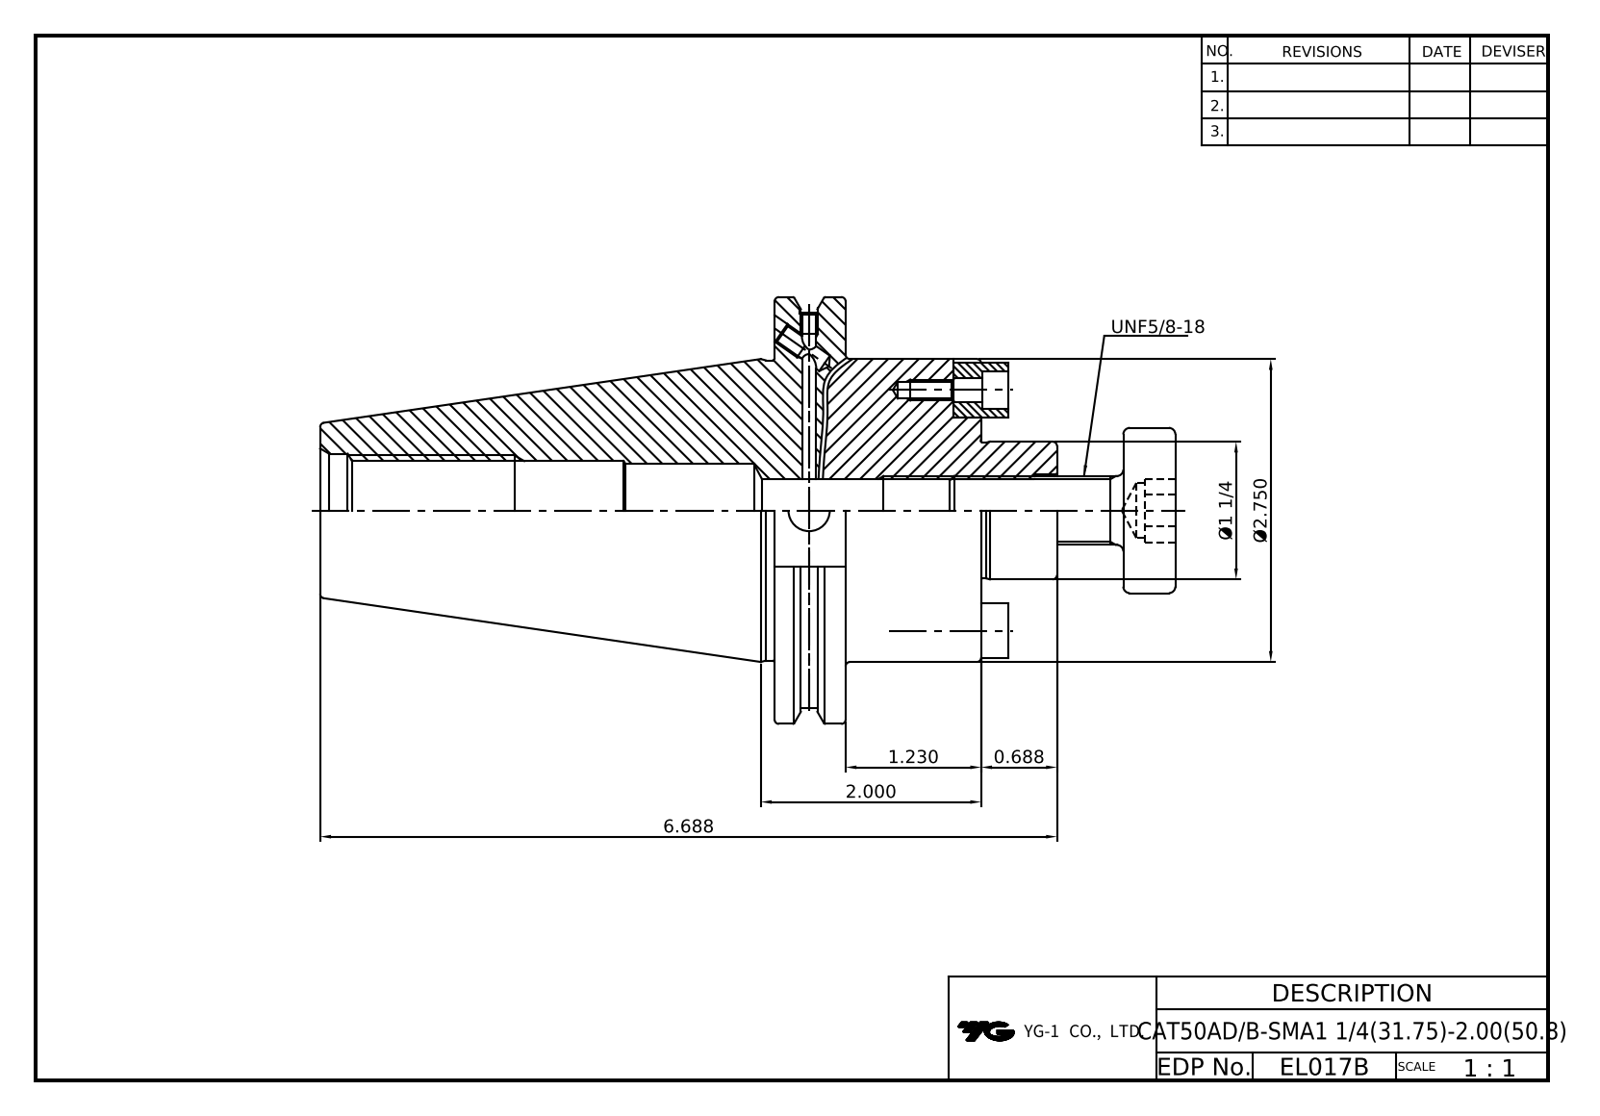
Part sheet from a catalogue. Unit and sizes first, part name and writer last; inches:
Units: inches
Overall size (bounding box): 7.554 × 3.875 × 3.728
Round holes (diameter × count): ⌀0.128 ×2, ⌀0.145 ×2, ⌀0.163 ×2, ⌀0.165 ×2, ⌀0.197 ×2, ⌀0.217 ×2, ⌀0.343 ×2, ⌀0.375 ×1, ⌀0.5 ×1, ⌀0.565 ×1, ⌀0.65 ×1, ⌀0.865 ×1
Round bosses / shafts (diameter × count): ⌀0.312 ×2, ⌀0.19 ×2, ⌀3.875 ×1, ⌀3.594 ×1, ⌀2.75 ×1, ⌀2.726 ×1, ⌀1.5 ×1, ⌀1.25 ×1
Partial cylindrical surfaces — rounded edges, fillets, slot ends (radius × count): R0.25 ×2
Main face-to-face distances: 0.625, 1.875, 1.25, 3.43, 2.804, 1.554, 0.25, 2.957, 2.332, 1.082
Hole centre spacings: 1.093, 1.094, 2.187, 2.187, 2.187
Volume: 28.73 in³ · Surface area: 101.2 in²
Bodies: 6 solids, 163 faces (88 planar, 43 cylindrical, 32 other)
Part name (STEP PRODUCT): LO-CAT50ADB-SMA31.75-50.8; COLLAR BOLT-UNF5_8-18x40L; DRIVE KEY-12.7x12.7x12.7; HEX'' WRENCH BOLT-UNC#10-24x1_2L
STEP written by: Autodesk Inventor 2025 (AP242_MANAGED_MODEL_BASED_3D_ENGINEERING_MIM_LF)
